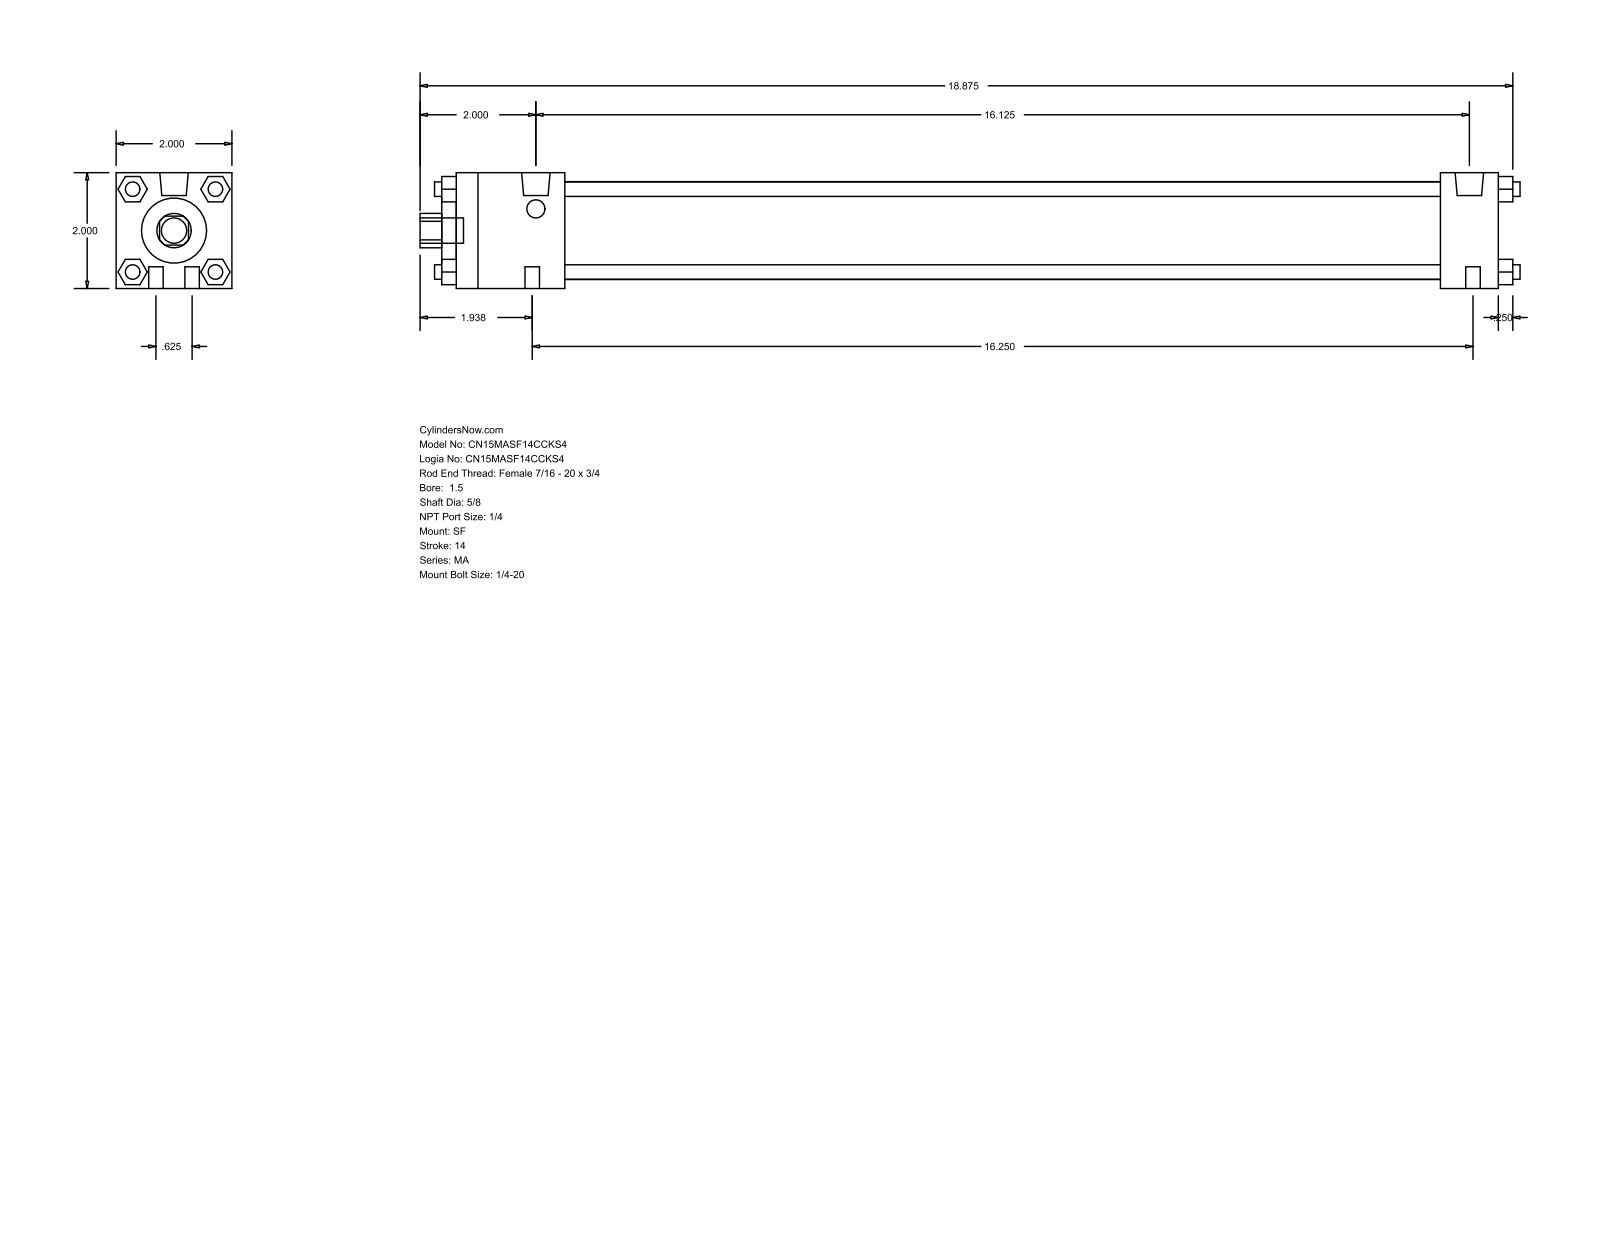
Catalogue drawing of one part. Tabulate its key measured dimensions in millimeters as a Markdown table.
| quantity | value |
| --- | --- |
| part name | MA_SF__0150_0.625 |
| STEP written by | GSSL Pune (CONFIG_CONTROL_DESIGN) |
| units | millimeters |
| bodies | 0 solids, 124 faces (94 planar, 30 cylindrical, 0 other) |
| overall size | 482.6 × 50.8 × 50.8 |
| round holes (diameter × count) | 15.88 × 1, 28.57 × 1, 42.93 × 1 |
| round bosses / shafts (diameter × count) | 6.35 × 8, 12.49 × 2, 7.94 × 2, 11.11 × 1 |
| partial cylindrical surfaces (radius × count) | 7.54 × 1 |
| main face-to-face distances | 50.8, 457.19, 47.62, 431.8, 384.18, 409.57, 25.39, 6.35, 53.97, 438.15 |
